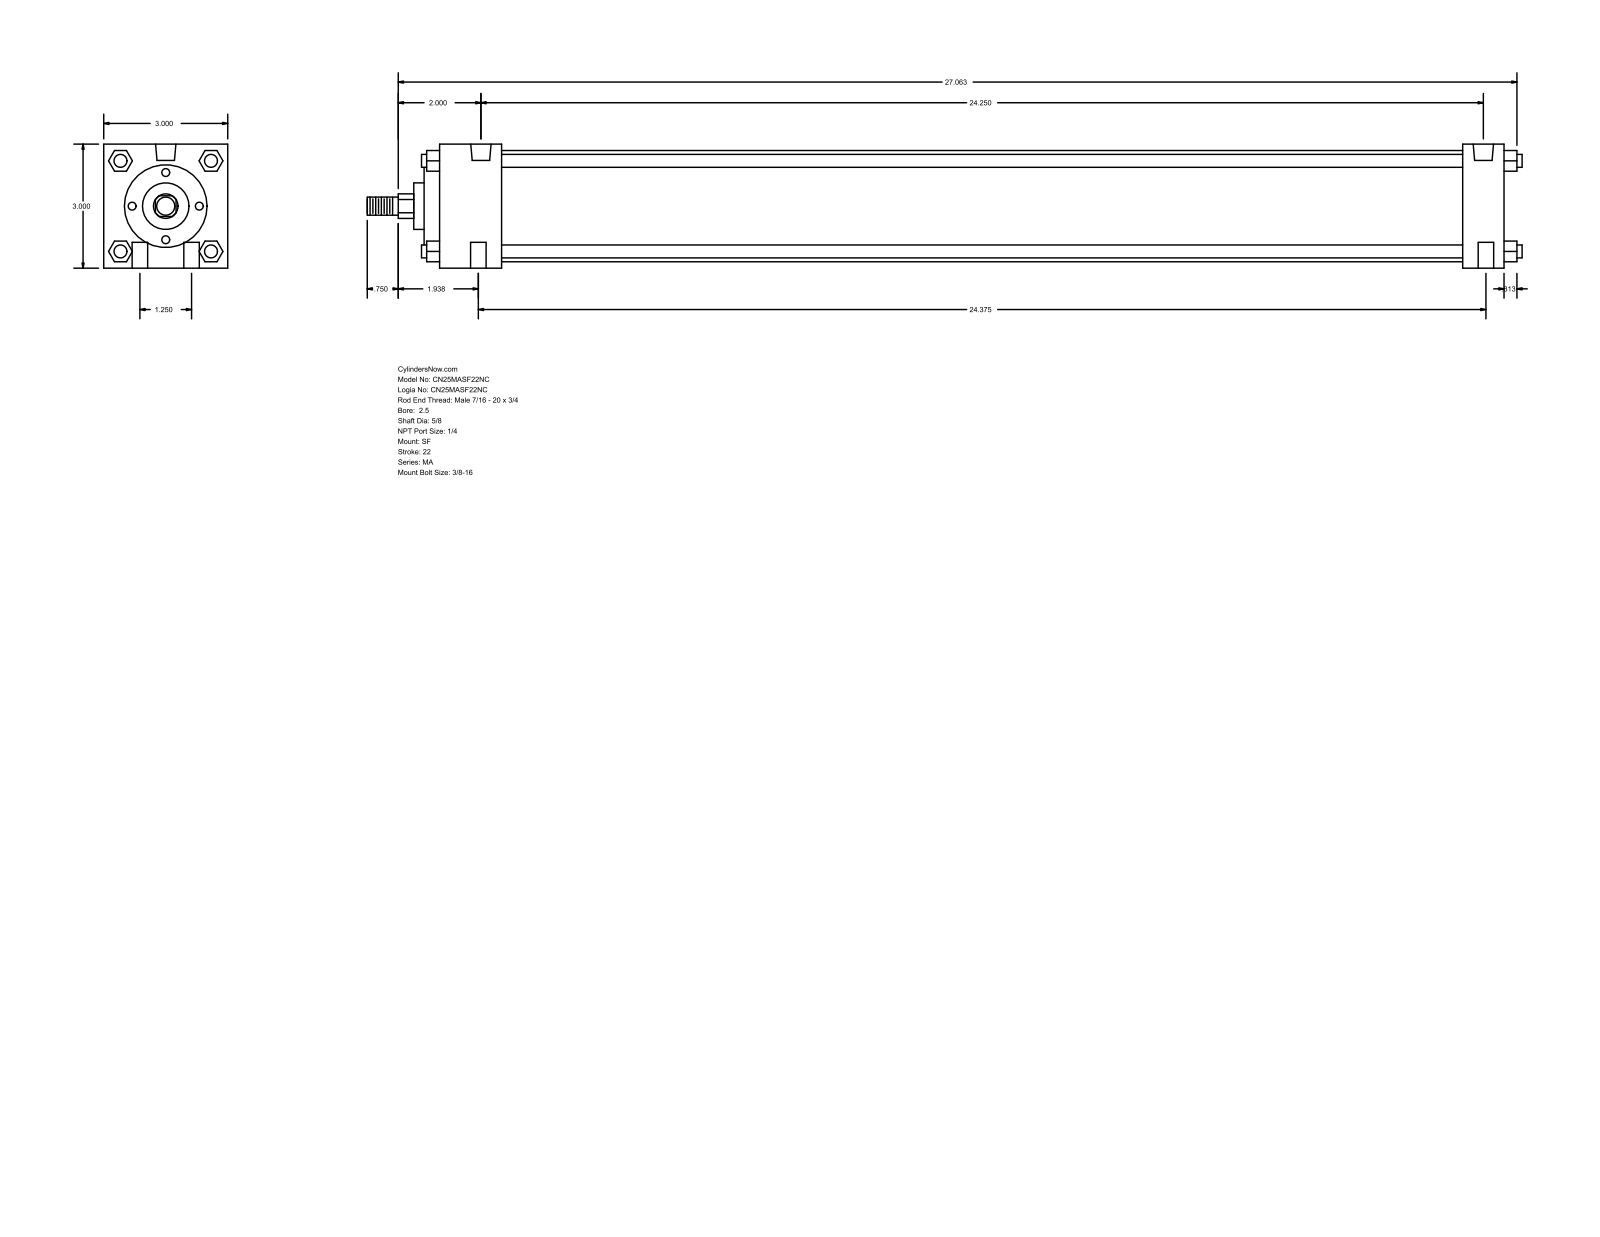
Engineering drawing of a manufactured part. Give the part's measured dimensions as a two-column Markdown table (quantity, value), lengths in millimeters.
| quantity | value |
| --- | --- |
| part name | MA_SF__0250_0.625 |
| STEP written by | GSSL Pune (CONFIG_CONTROL_DESIGN) |
| units | millimeters |
| bodies | 0 solids, 126 faces (95 planar, 31 cylindrical, 0 other) |
| overall size | 709.61 × 76.2 × 76.2 |
| round holes (diameter × count) | 9.53 × 4, 7.94 × 2, 12.49 × 2 |
| round bosses / shafts (diameter × count) | 7.94 × 4, 68.33 × 1, 50.8 × 1, 28.57 × 1, 15.88 × 1, 11.11 × 1 |
| partial cylindrical surfaces (radius × count) | 7.54 × 1 |
| main face-to-face distances | 76.2, 654.05, 25.4, 628.65, 38.1, 590.55, 615.95, 12.7, 9.52, 47.62 |
| hole center spacings | 15.96, 617.74, 31.76, 615.95, 619.13, 619.94 |
